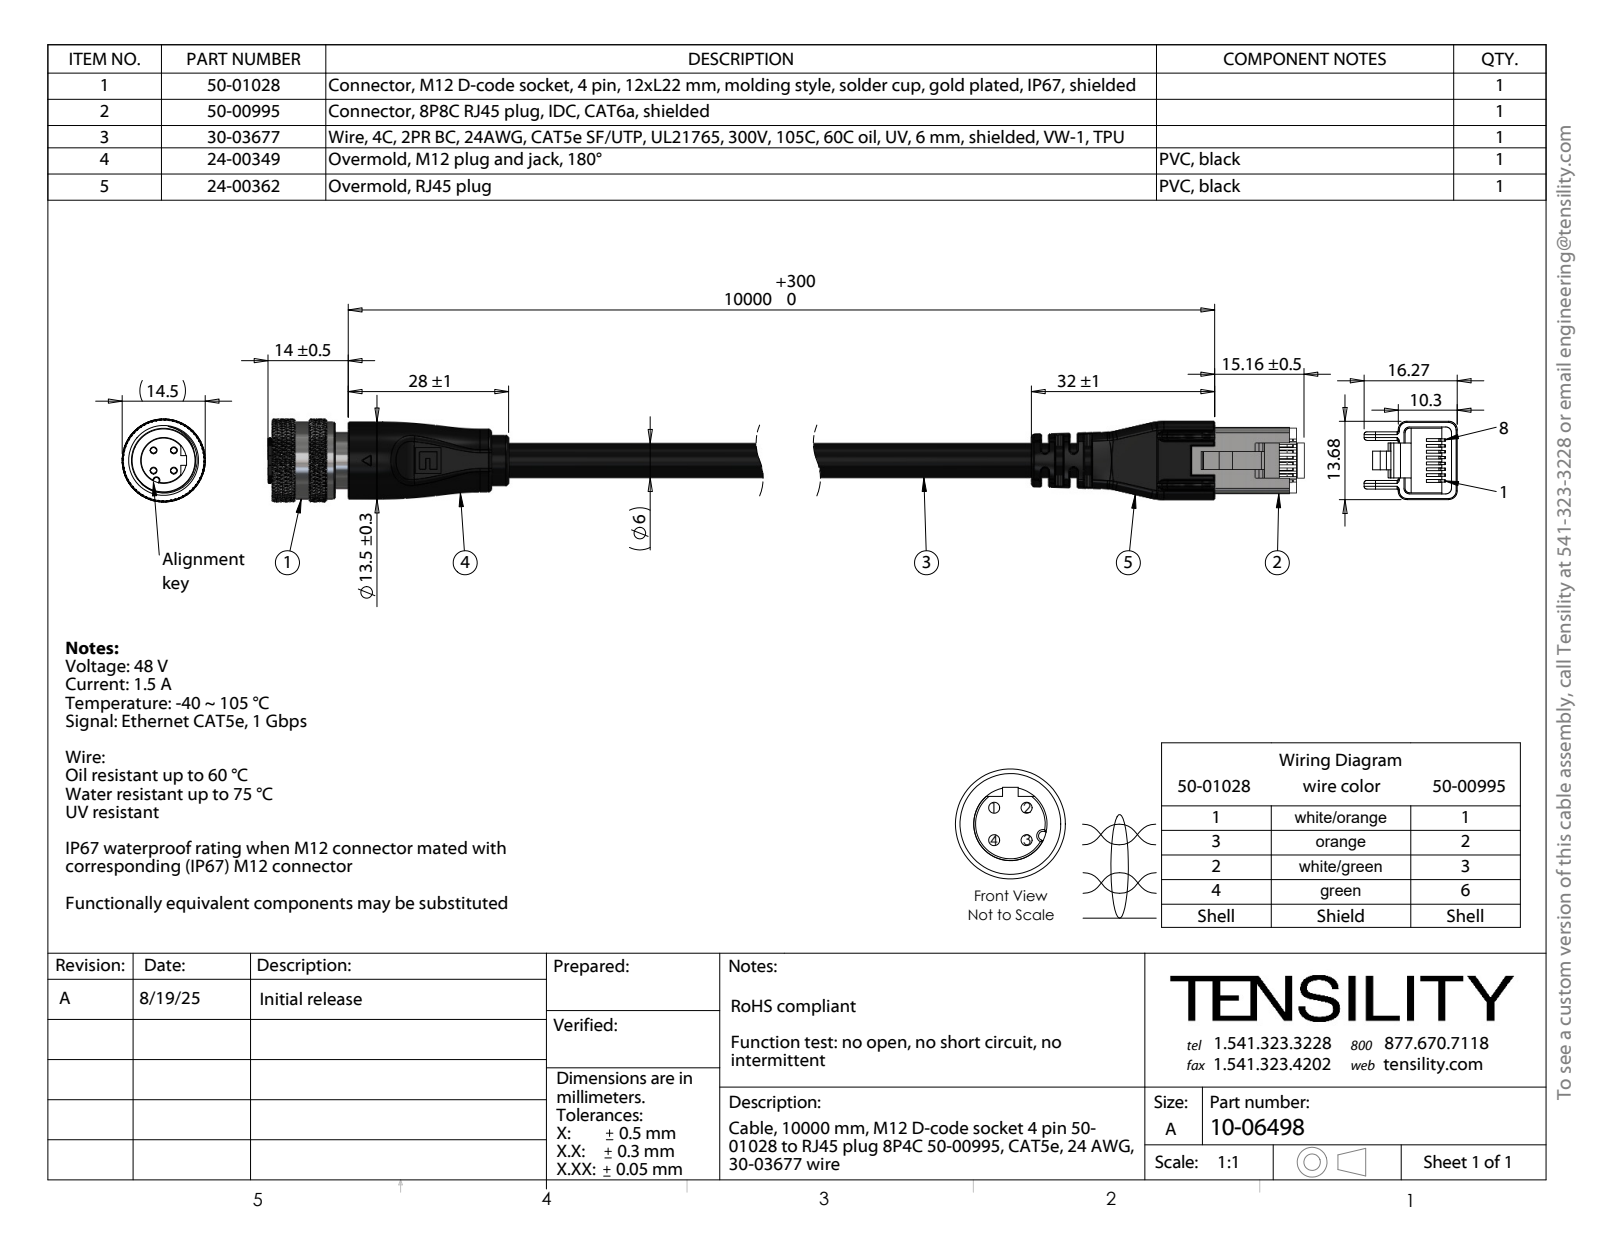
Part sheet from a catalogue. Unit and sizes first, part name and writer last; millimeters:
Units: millimetres
Overall size (bounding box): 229.11 × 18.37 × 14.5
Round holes (diameter × count): ⌀0.2 ×28, ⌀1.05 ×4, ⌀1.1 ×4, ⌀1.2 ×4, ⌀3.16 ×1, ⌀3.21 ×1, ⌀3.56 ×1, ⌀9 ×1, ⌀10 ×1, ⌀11.2 ×1
Round bosses / shafts (diameter × count): ⌀1.6 ×4, ⌀1.5 ×4, ⌀13.5 ×1, ⌀11 ×1, ⌀10.6 ×1, ⌀10.5 ×1, ⌀9.8 ×1, ⌀9.7 ×1
Partial cylindrical surfaces — rounded edges, fillets, slot ends (radius × count): R0.2 ×11, R0.1 ×10, R0.5 ×10, R1.5 ×10, R0.62 ×8, R0.4 ×6, R1 ×5, R10 ×4
Main face-to-face distances: 1.25, 1, 2.5, 3.75, 9.3, 5, 1.5, 199.5, 12.68, 8.5
Hole centre spacings: 1.91, 0.36, 2.09, 1.06, 0.89, 1.08, 1.24, 1.8
Volume: 14 248 mm³ · Surface area: 29 704 mm²
Bodies: 55 solids, 3967 faces (546 planar, 928 cylindrical, 2493 other)
Part name (STEP PRODUCT): 50-01028-05_默认; 50-01028_默认; 50-01028-03_默认; 24-00362 (+7 more)
STEP written by: SolidWorks 2025 (CONFIG_CONTROL_DESIGN)
